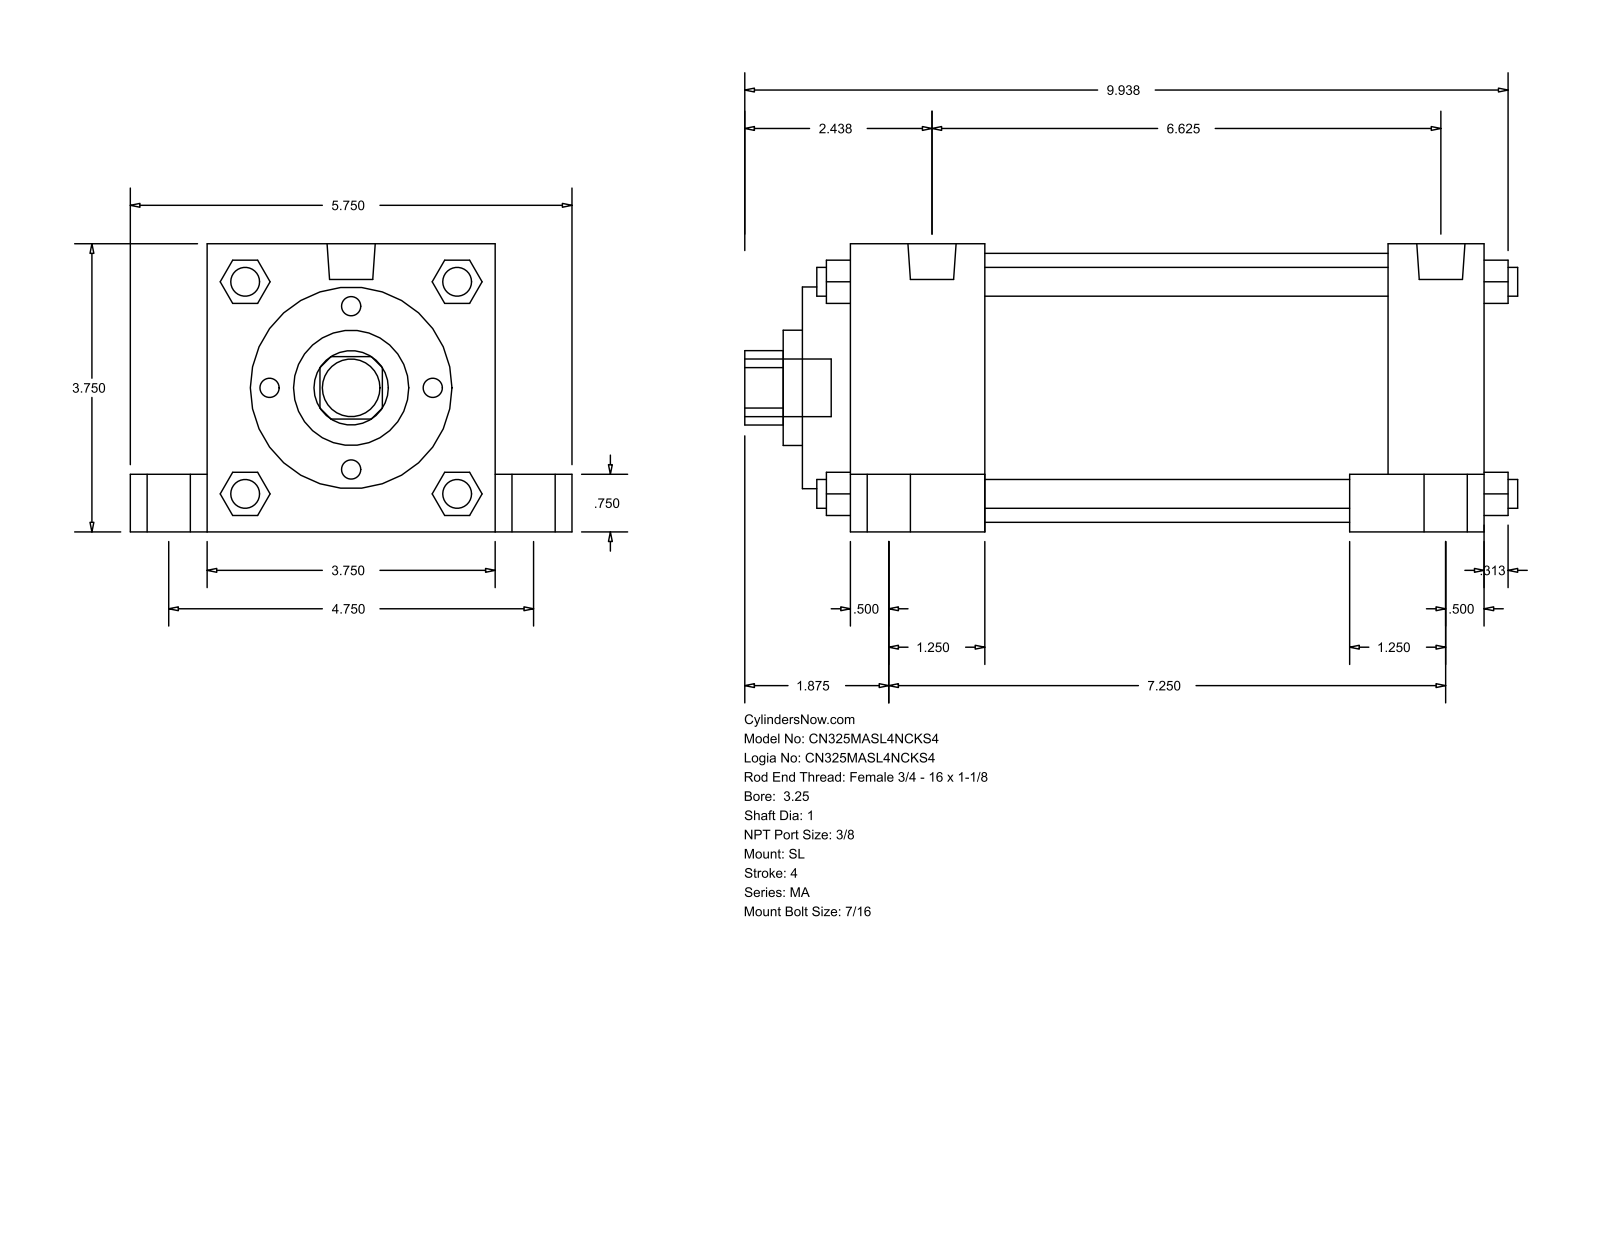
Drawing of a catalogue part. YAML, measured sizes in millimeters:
part_name: "MA_SL__0325_1"
step_written_by: "GSSL Pune (CONFIG_CONTROL_DESIGN)"
units: millimeters
bodies: {solids: 0, faces: 150, planar: 113, cylindrical: 37, other: 0}
overall_size: [255.59, 146.05, 95.25]
round_holes:
  - {diameter: 25.4, count: 1}
  - {diameter: 38.1, count: 1}
  - {diameter: 66.67, count: 1}
  - {diameter: 88.9, count: 1}
round_bosses_or_shafts:
  - {diameter: 20.64, count: 4}
  - {diameter: 14.29, count: 4}
  - {diameter: 11.11, count: 4}
  - {diameter: 9.53, count: 4}
  - {diameter: 15.93, count: 2}
  - {diameter: 19.05, count: 1}
partial_cylinders:
  - {radius: 12.29, count: 1}
face_to_face_distances: [95.24, 209.55, 15.87, 25.41, 120.65, 225.42, 19.05, 177.8, 31.75, 44.46]
